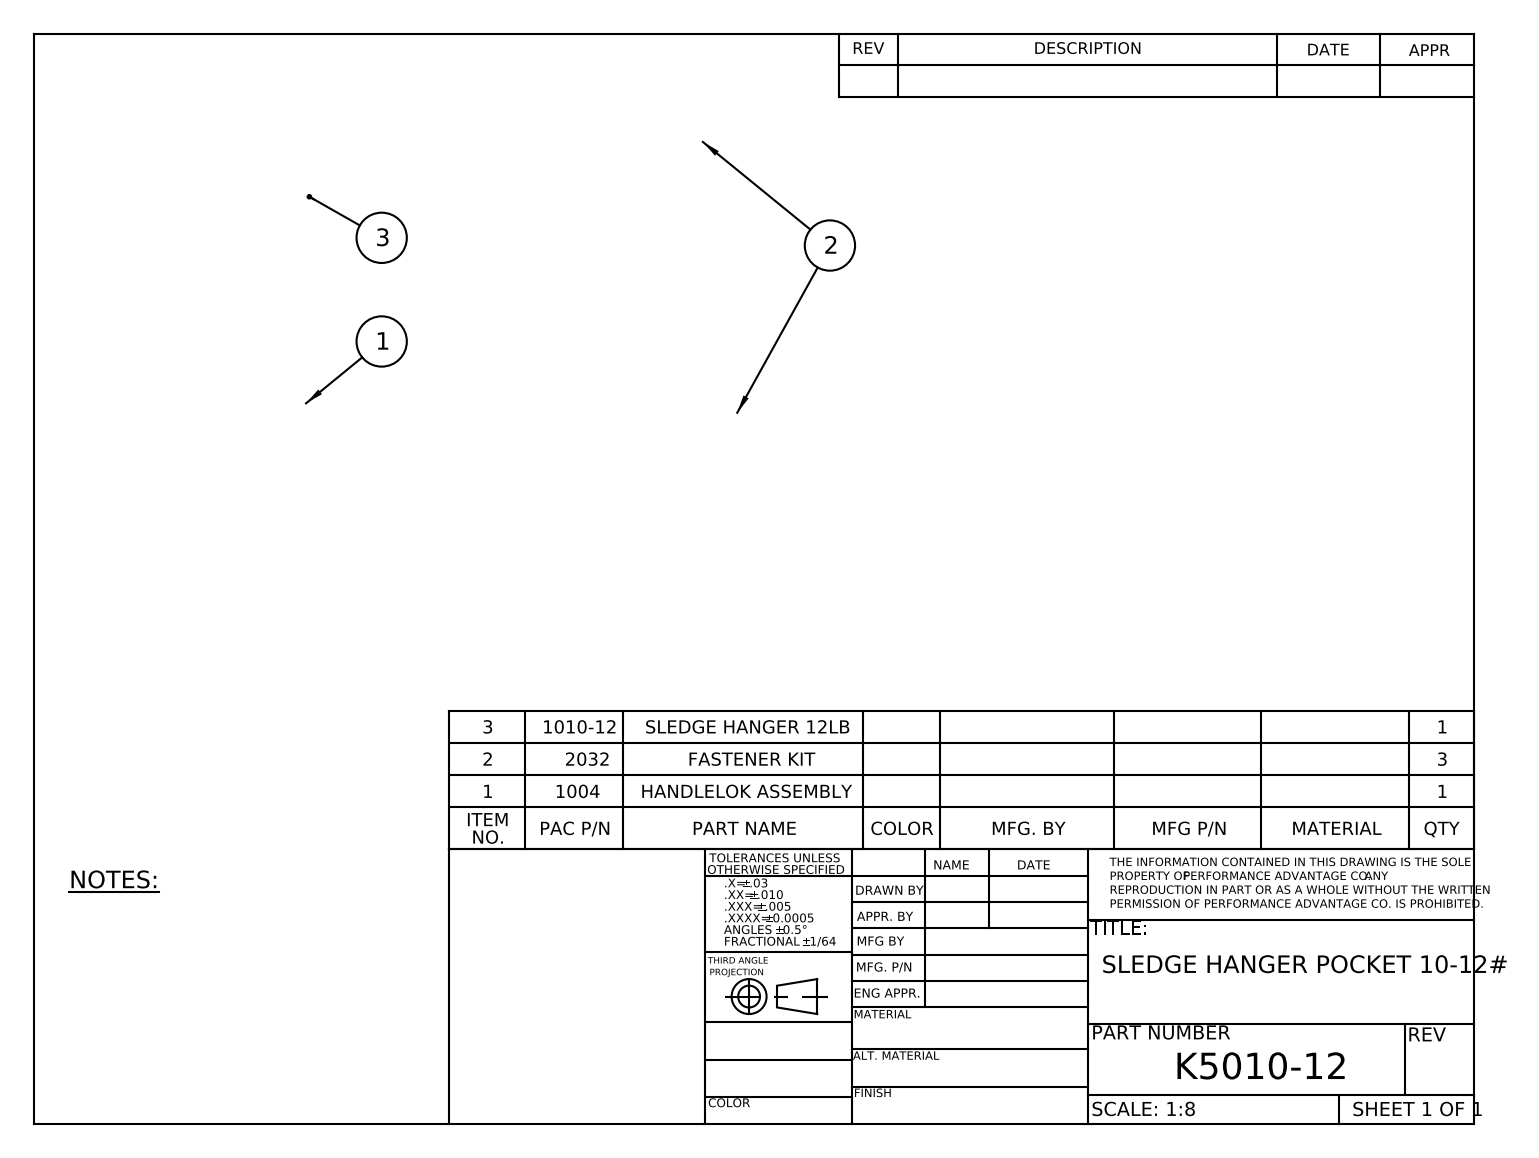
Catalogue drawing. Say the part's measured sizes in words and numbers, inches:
The part is named "2069LN_MSHXNUT 0.250-20-S-N; 2031_CR-FHMS 0.25-20x0.75x0.75-N; 2032; 2032_3.875\" spacing (+8 more)". Its 3-D file was written by "SolidWorks 2010 (CONFIG_CONTROL_DESIGN)". It is 25 solids with 1563 faces: 592 planar, 513 cylindrical and 458 other. Overall it measures 35.32 by 8.05 by 4.255 inches. Its volume is 101.9 cubic inches and its surface area 463.9 square inches. Round holes: 7 of diameter 0.25, 6 of diameter 0.201, 6 of diameter 0.266, 6 of diameter 0.269, 4 of diameter 0.17, 1 of diameter 0.156, 1 of diameter 0.156, 1 of diameter 0.313. Round bosses or shafts: 6 of diameter 0.452, 6 of diameter 0.404, 4 of diameter 0.187, 4 of diameter 0.162, 3 of diameter 0.205, 1 of diameter 0.625, 1 of diameter 0.205. Partial cylindrical surfaces (rounded edges, fillets, slot ends): 68 of radius 0.016, 32 of radius 0.041, 16 of radius 0.25, 12 of radius 0.125, 11 of radius 0.062, 8 of radius 0.063, 8 of radius 0.4, 7 of radius 0.068. The main face-to-face distances are 0.4, 0.25, 3.15, 2.75, 2.68, 2.43, 0.25, 7.8, 3, 0.125. The hole center spacings are 0.825, 1.317, 3.058, 17.797, 0.562, 1, 1.147, 1.875.
